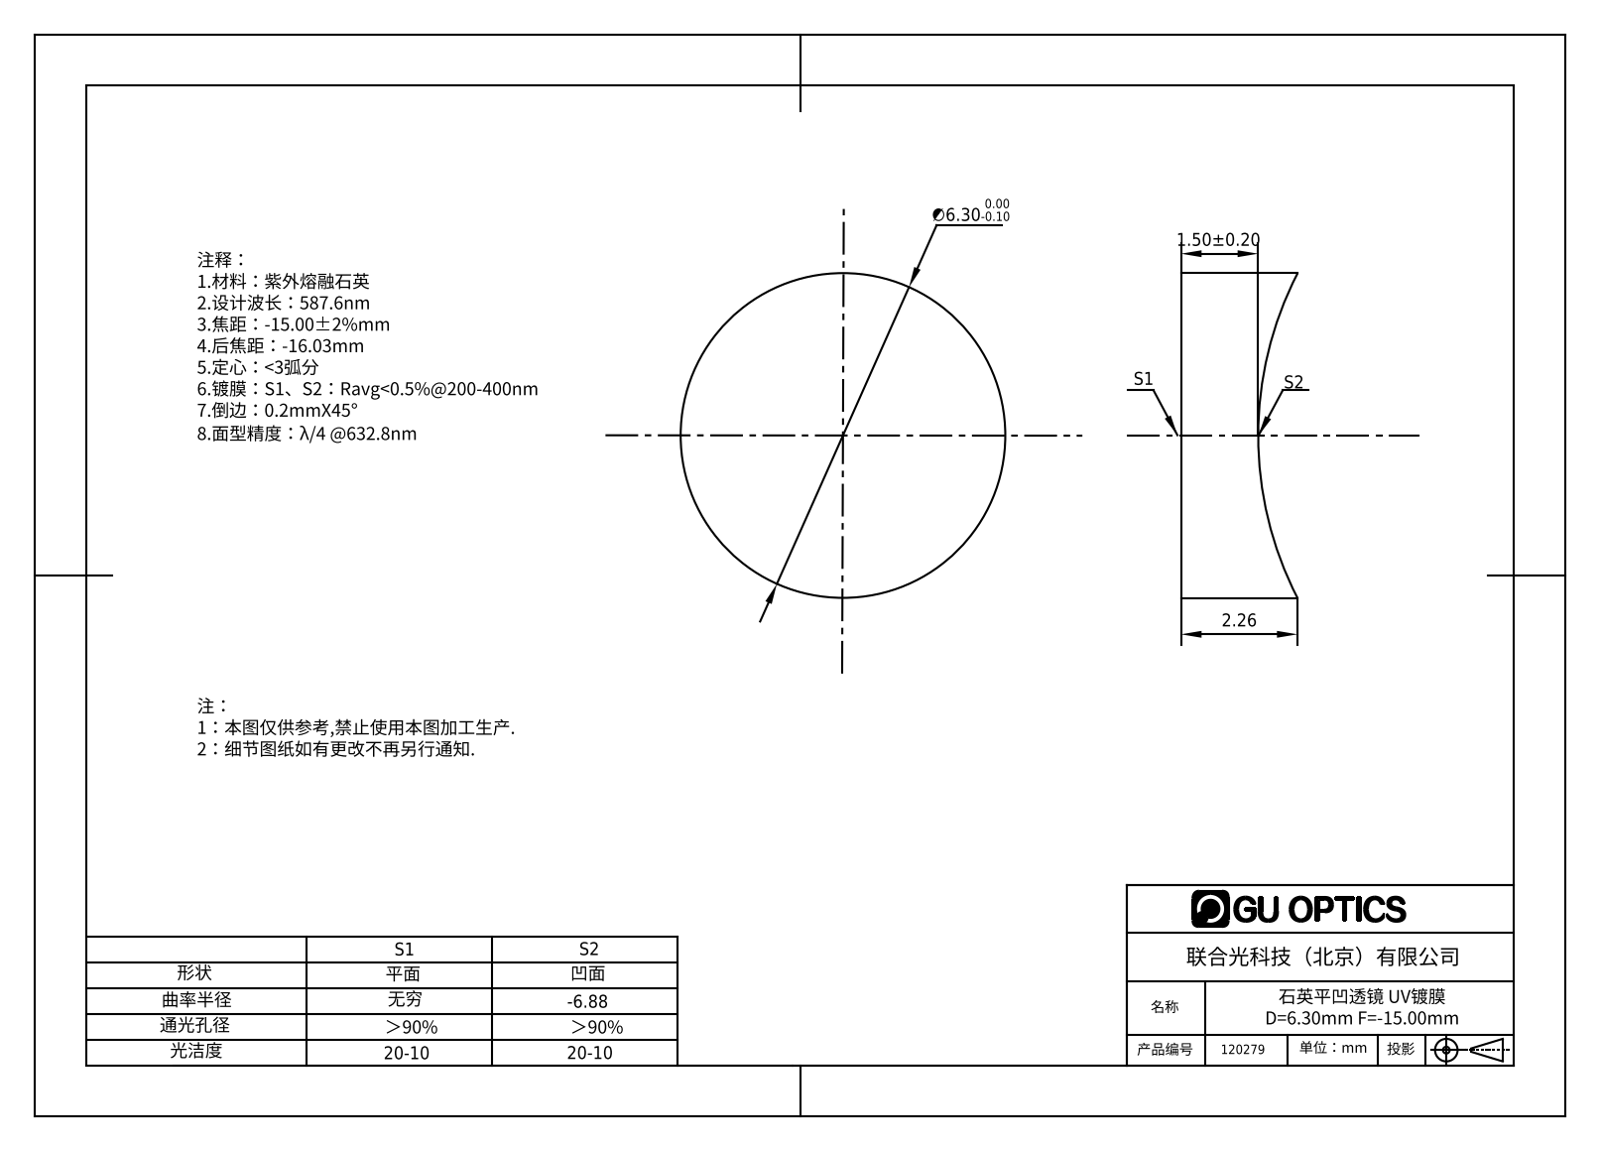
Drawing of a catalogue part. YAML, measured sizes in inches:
part_name: "120246"
step_written_by: "SolidWorks 2016 (AUTOMOTIVE_DESIGN)"
units: inches
bodies: {solids: 1, faces: 5, planar: 1, cylindrical: 2, other: 2}
overall_size: [0.248, 0.248, 0.089]
volume: 0.004
surface_area: 0.169
round_bosses_or_shafts:
  - {diameter: 0.248, count: 1}
